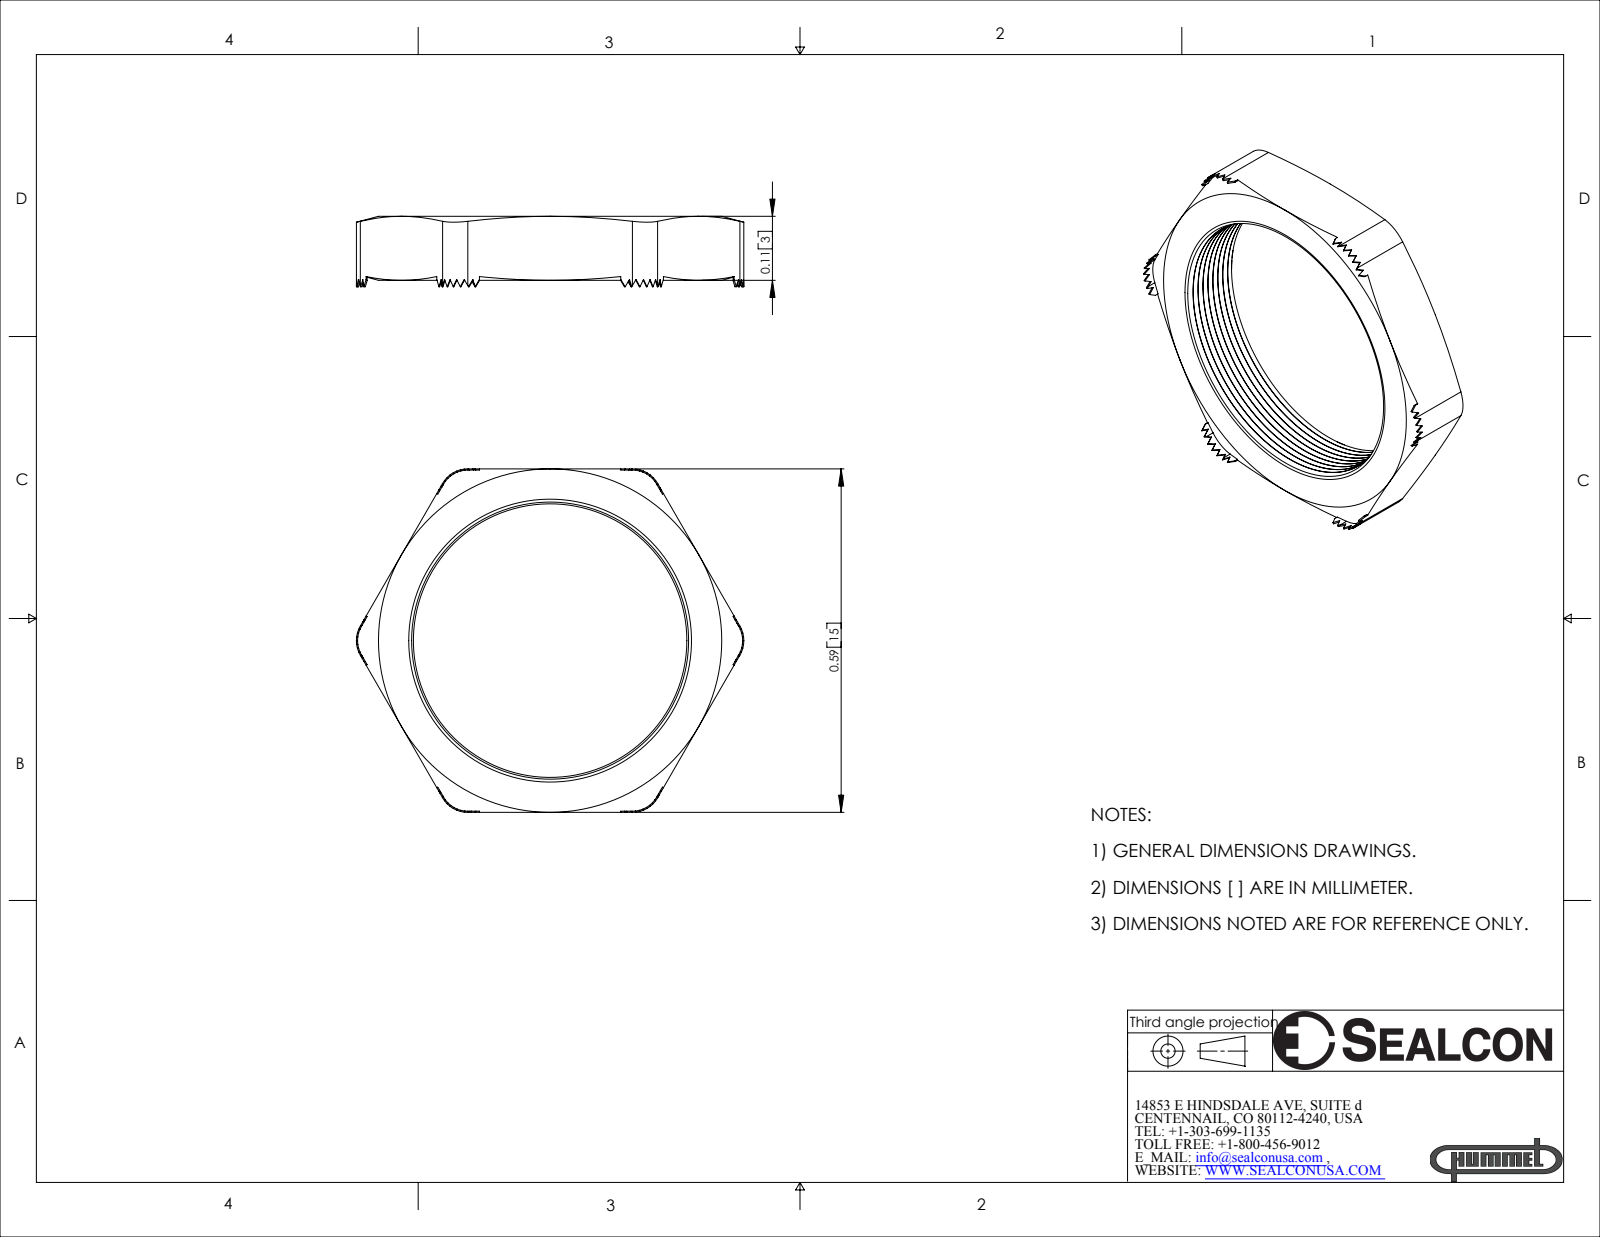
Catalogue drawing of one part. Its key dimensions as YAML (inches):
part_name: "NM-12-BE"
step_written_by: "SolidWorks 2007 (CONFIG_CONTROL_DESIGN)"
units: inches
bodies: {solids: 1, faces: 200, planar: 116, cylindrical: 30, other: 54}
overall_size: [0.666, 0.59, 0.121]
volume: 0.013
surface_area: 0.784
round_holes:
  - {diameter: 0.47, count: 1}
partial_cylinders:
  - {radius: 0.048, count: 6}
  - {radius: 0.05, count: 6}
face_to_face_distances: [0.59, 0.11, 0.588, 0.586, 0.023, 0.035, 0.023, 0.043, 0.032, 0.055]
